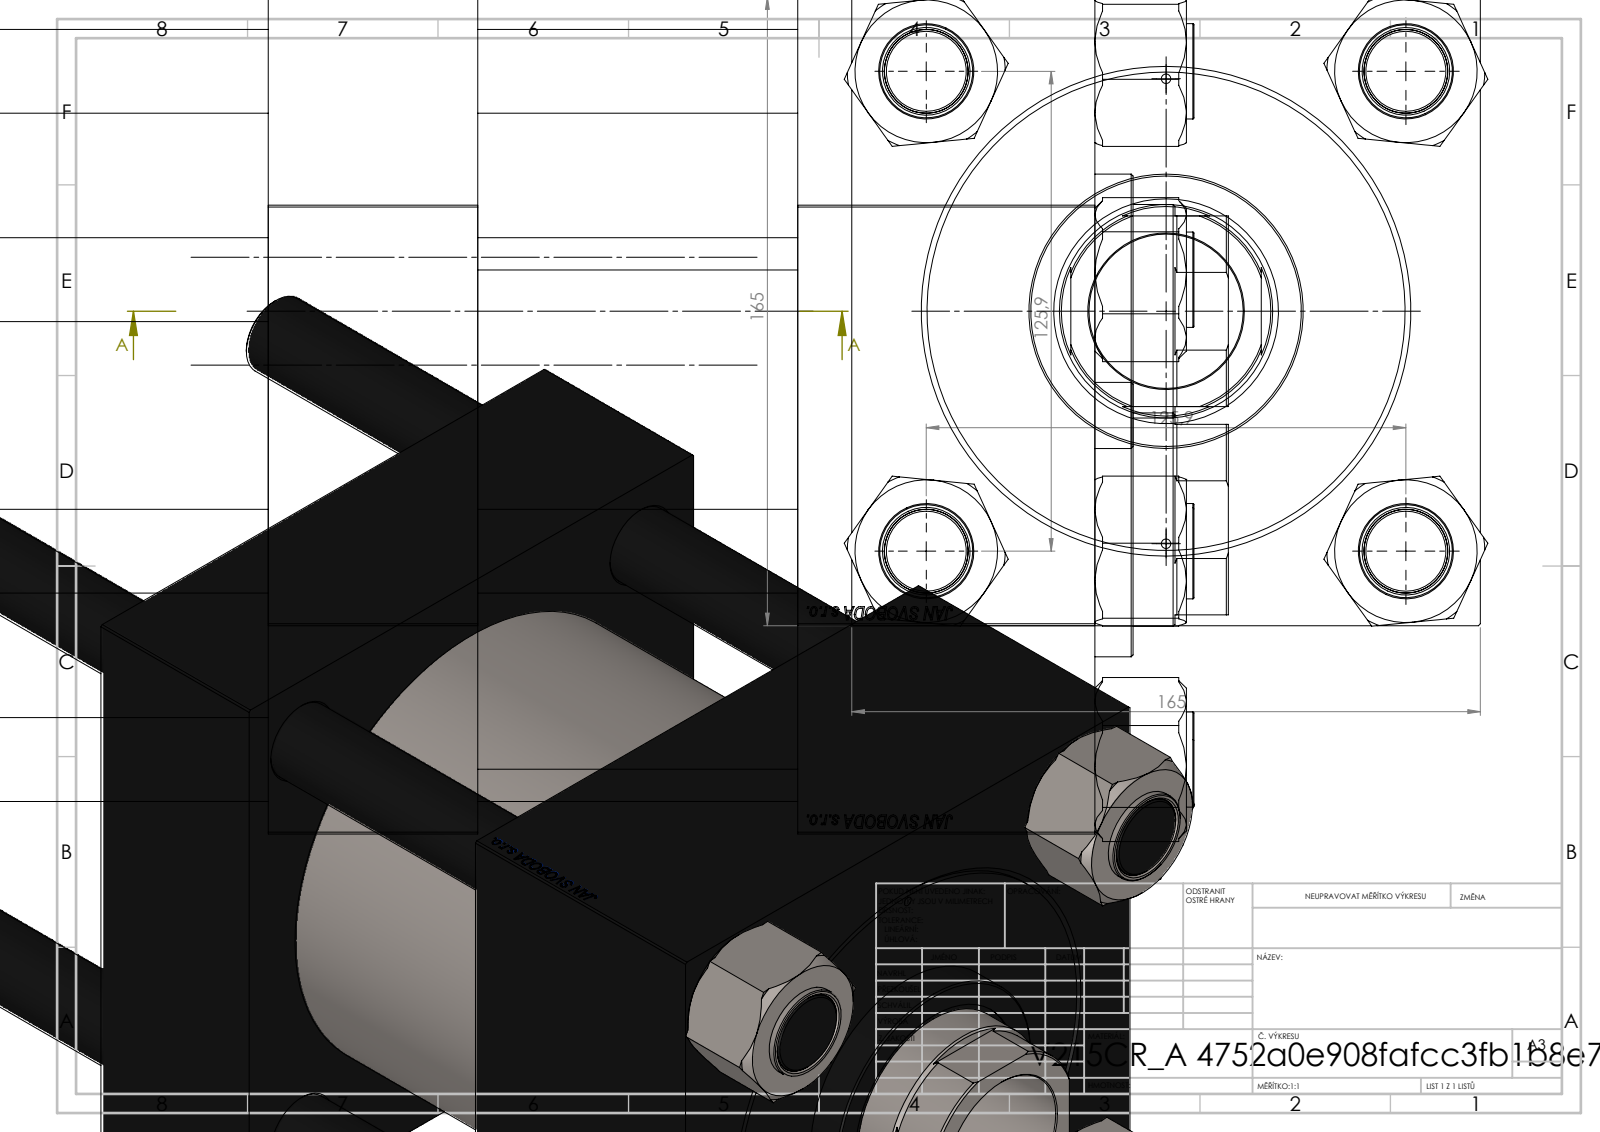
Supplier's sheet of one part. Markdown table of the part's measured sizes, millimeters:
| quantity | value |
| --- | --- |
| part name | CR025_012_A_0_G_A_G_M_020_+#_##_TYCINKA; V215CR_VCP; NUT_M5; V215CR_BODY_A (+1 more) |
| STEP written by | SolidWorks 2019 (CONFIG_CONTROL_DESIGN) |
| units | millimeters |
| bodies | 11 solids, 1187 faces (568 planar, 83 cylindrical, 536 other) |
| overall size | 333 × 168.94 × 165.27 |
| volume | 4 665 000 mm³ |
| surface area | 550 122 mm² |
| round holes (diameter × count) | 22 × 4, 2.5 × 2, 7 × 2, 45 × 2, 27 × 1, 32.24 × 1, 40.5 × 1, 56 × 1, 59 × 1, 96 × 1, 125 × 1, 125.5 × 1 |
| round bosses / shafts (diameter × count) | 25 × 4, 131 × 1, 72 × 1 |
| partial cylindrical surfaces (radius × count) | 27 × 1 |
| main face-to-face distances | 165, 55, 162, 217, 139, 84, 78, 188.3, 133.3, 49.3 |
| hole center spacings | 62.98, 89.02, 125.9, 139.02, 61, 178.05, 122, 138.5 |
